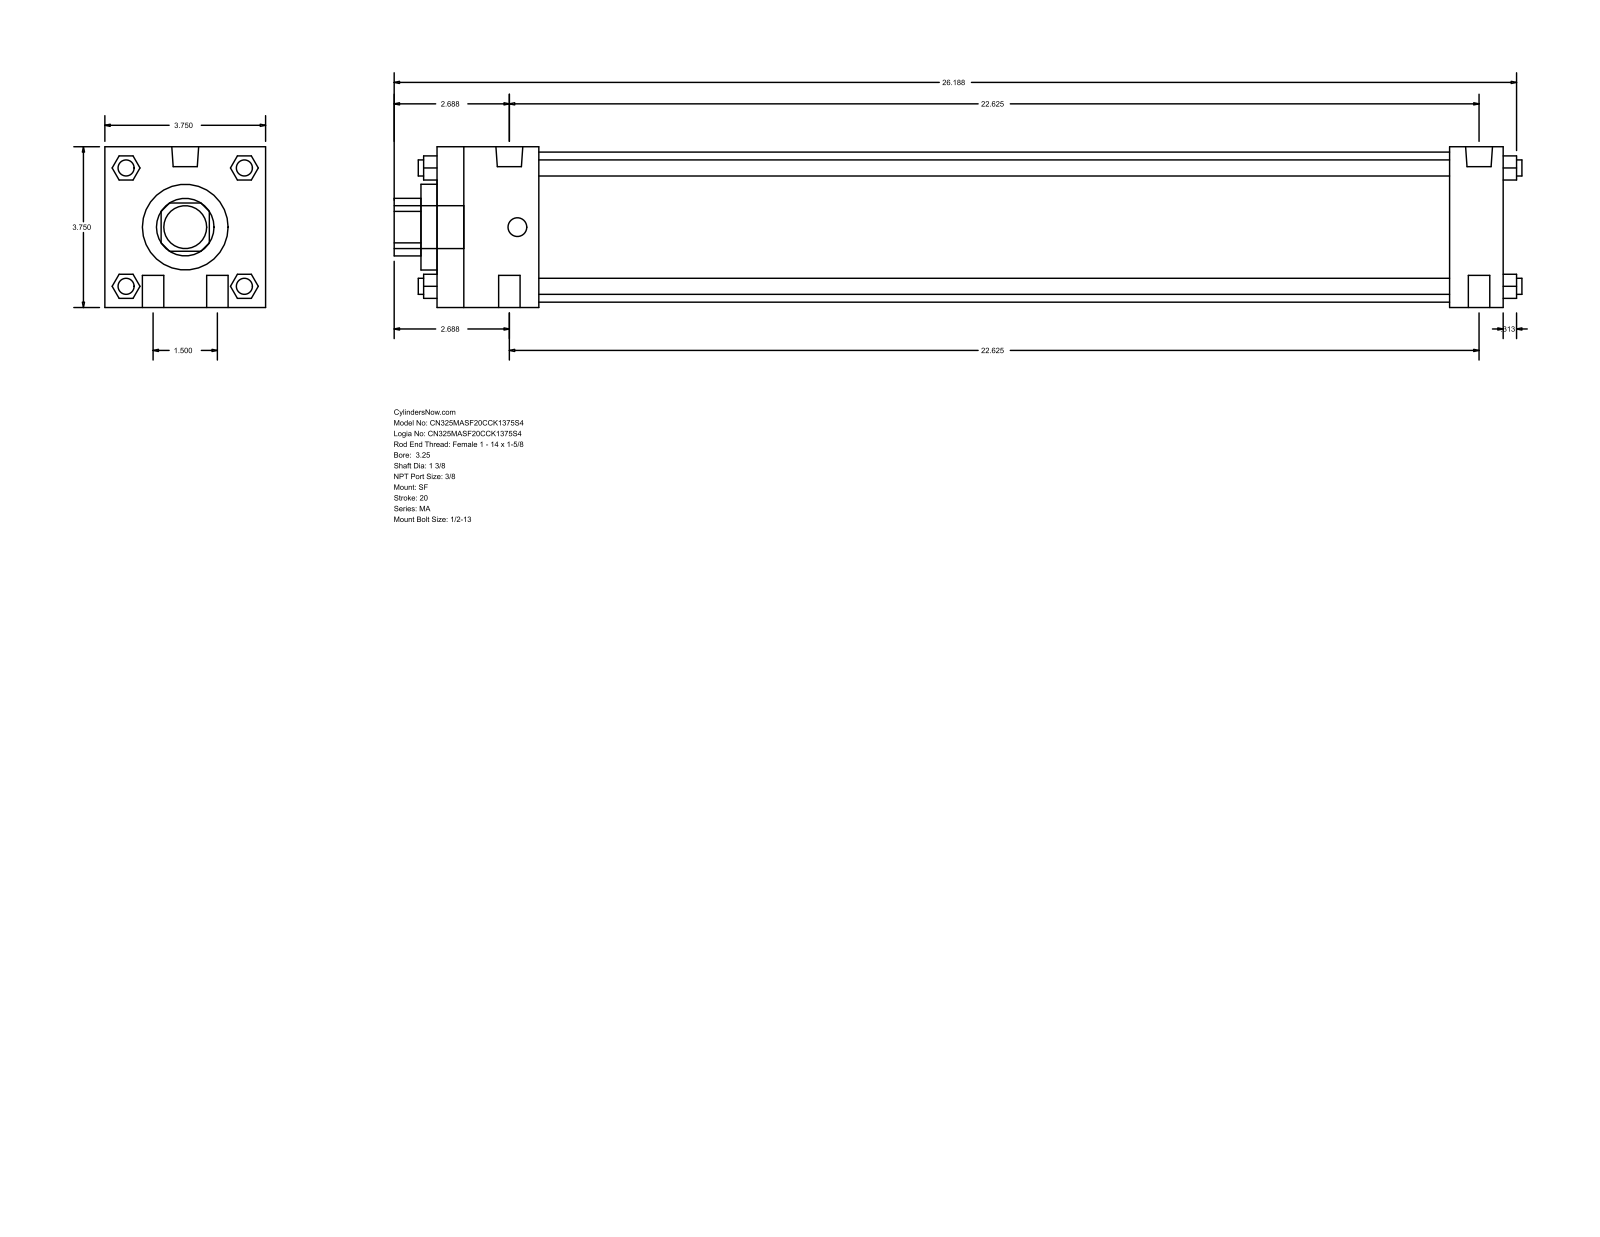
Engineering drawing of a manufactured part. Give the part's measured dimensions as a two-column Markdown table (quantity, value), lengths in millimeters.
| quantity | value |
| --- | --- |
| part name | MA_SF__0325_1.375 |
| STEP written by | GSSL Pune (CONFIG_CONTROL_DESIGN) |
| units | millimeters |
| bodies | 0 solids, 124 faces (94 planar, 30 cylindrical, 0 other) |
| overall size | 668.34 × 95.25 × 95.25 |
| round holes (diameter × count) | 34.92 × 1, 50.8 × 1, 88.9 × 1 |
| round bosses / shafts (diameter × count) | 12.7 × 4, 9.53 × 4, 15.93 × 2, 11.11 × 2, 25.4 × 1 |
| partial cylindrical surfaces (radius × count) | 17.06 × 1 |
| main face-to-face distances | 95.24, 631.83, 600.08, 31.75, 60.32, 539.76, 571.51, 9.52, 69.84, 609.6 |
